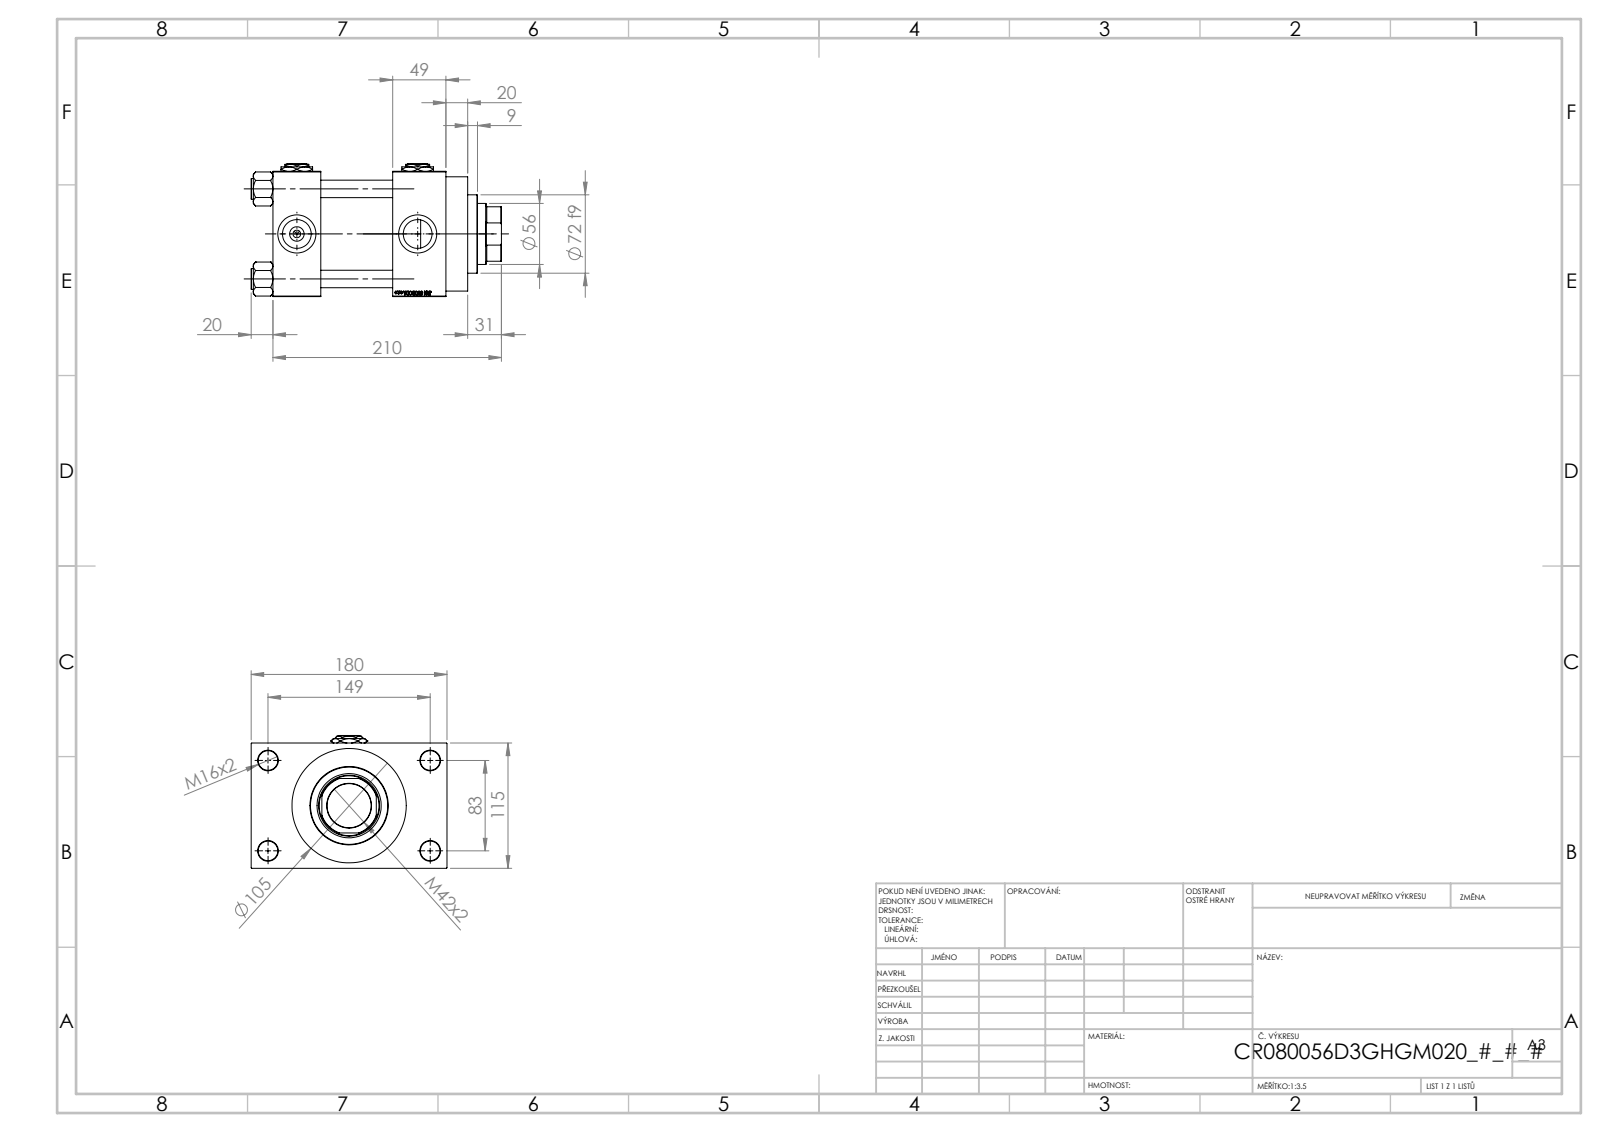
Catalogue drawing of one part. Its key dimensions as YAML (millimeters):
part_name: "V215CR_D_TYCINKA; NUT_M5_D; V215CR_D_Body; Zatka_pro_OIL_PORT (+2 more)"
step_written_by: "SolidWorks 2019 (CONFIG_CONTROL_DESIGN)"
units: millimeters
bodies: {solids: 13, faces: 1251, planar: 592, cylindrical: 97, other: 562}
overall_size: [230, 180, 122]
volume: 2087000
surface_area: 317251
round_holes:
  - {diameter: 16, count: 4}
  - {diameter: 18, count: 4}
  - {diameter: 26.44, count: 4}
  - {diameter: 35, count: 4}
  - {diameter: 7, count: 3}
  - {diameter: 40.5, count: 1}
  - {diameter: 56, count: 1}
  - {diameter: 59, count: 1}
  - {diameter: 61, count: 1}
  - {diameter: 72, count: 1}
  - {diameter: 80, count: 1}
round_bosses_or_shafts:
  - {diameter: 19, count: 4}
  - {diameter: 105, count: 1}
  - {diameter: 86, count: 1}
partial_cylinders:
  - {radius: 27, count: 1}
face_to_face_distances: [115, 66, 110, 44, 159, 49, 32.5, 147.5, 20, 69]
hole_center_spacings: [33.15, 58.48, 82.7, 85.28, 89.24, 115.85, 142.43, 83]
